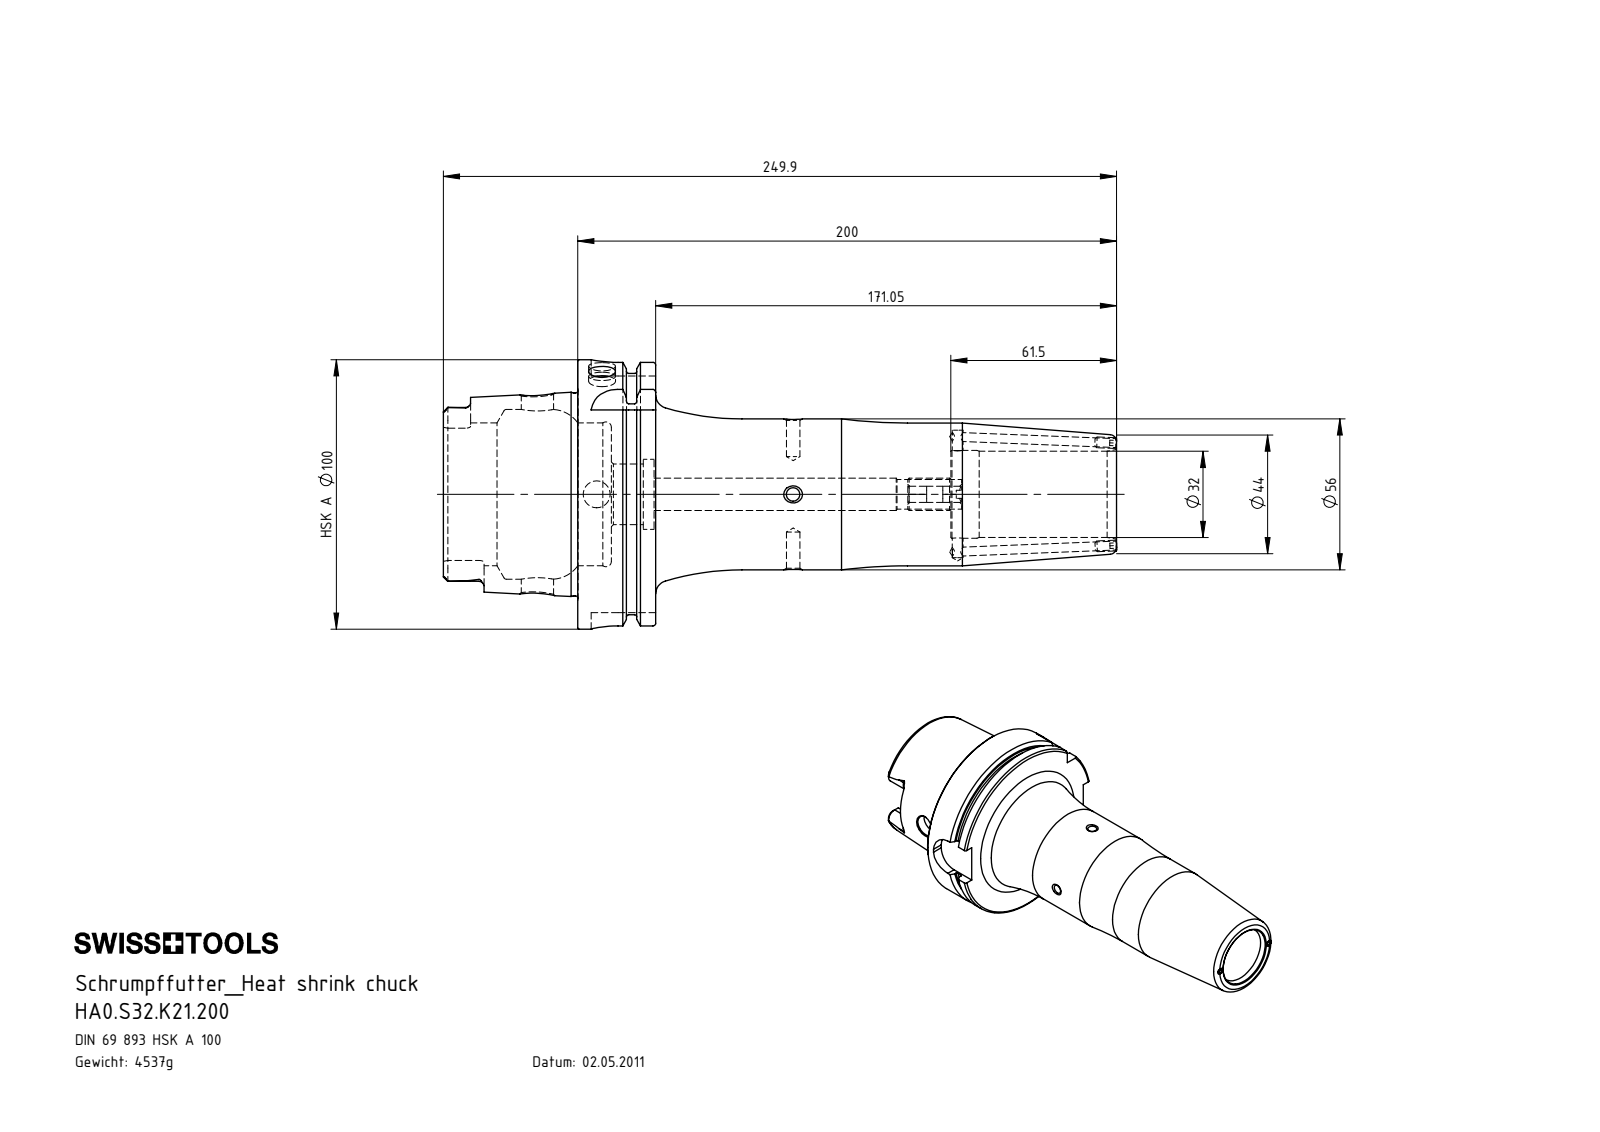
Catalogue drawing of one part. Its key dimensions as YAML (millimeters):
part_name: "HA0.S32.K21.200; HA0-S32.K21.200_C_Fertigbearbeitung; ERU-AN5.K01.020_A; ERU-CJ3.001.008"
step_written_by: "SolidWorks 2017 (CONFIG_CONTROL_DESIGN)"
units: millimeters
bodies: {solids: 4, faces: 303, planar: 95, cylindrical: 86, other: 122}
overall_size: [250, 100, 100]
volume: 577920
surface_area: 90289
round_holes:
  - {diameter: 10, count: 3}
  - {diameter: 3.3, count: 2}
  - {diameter: 5, count: 2}
  - {diameter: 12, count: 2}
  - {diameter: 4, count: 1}
  - {diameter: 6, count: 1}
  - {diameter: 11, count: 1}
  - {diameter: 22.5, count: 1}
  - {diameter: 26, count: 1}
  - {diameter: 32, count: 1}
  - {diameter: 32.6, count: 1}
  - {diameter: 53, count: 1}
round_bosses_or_shafts:
  - {diameter: 4, count: 2}
  - {diameter: 100, count: 1}
  - {diameter: 91.95, count: 1}
  - {diameter: 75.26, count: 1}
  - {diameter: 56, count: 1}
partial_cylinders:
  - {radius: 1.9, count: 6}
  - {radius: 4.88, count: 4}
  - {radius: 10, count: 4}
face_to_face_distances: [28.95, 12.45, 16.5, 49.9, 62.35, 78.85, 188.4, 138.5, 126.05, 109.55]
hole_center_spacings: [61.05, 72.95, 94.95, 156]
